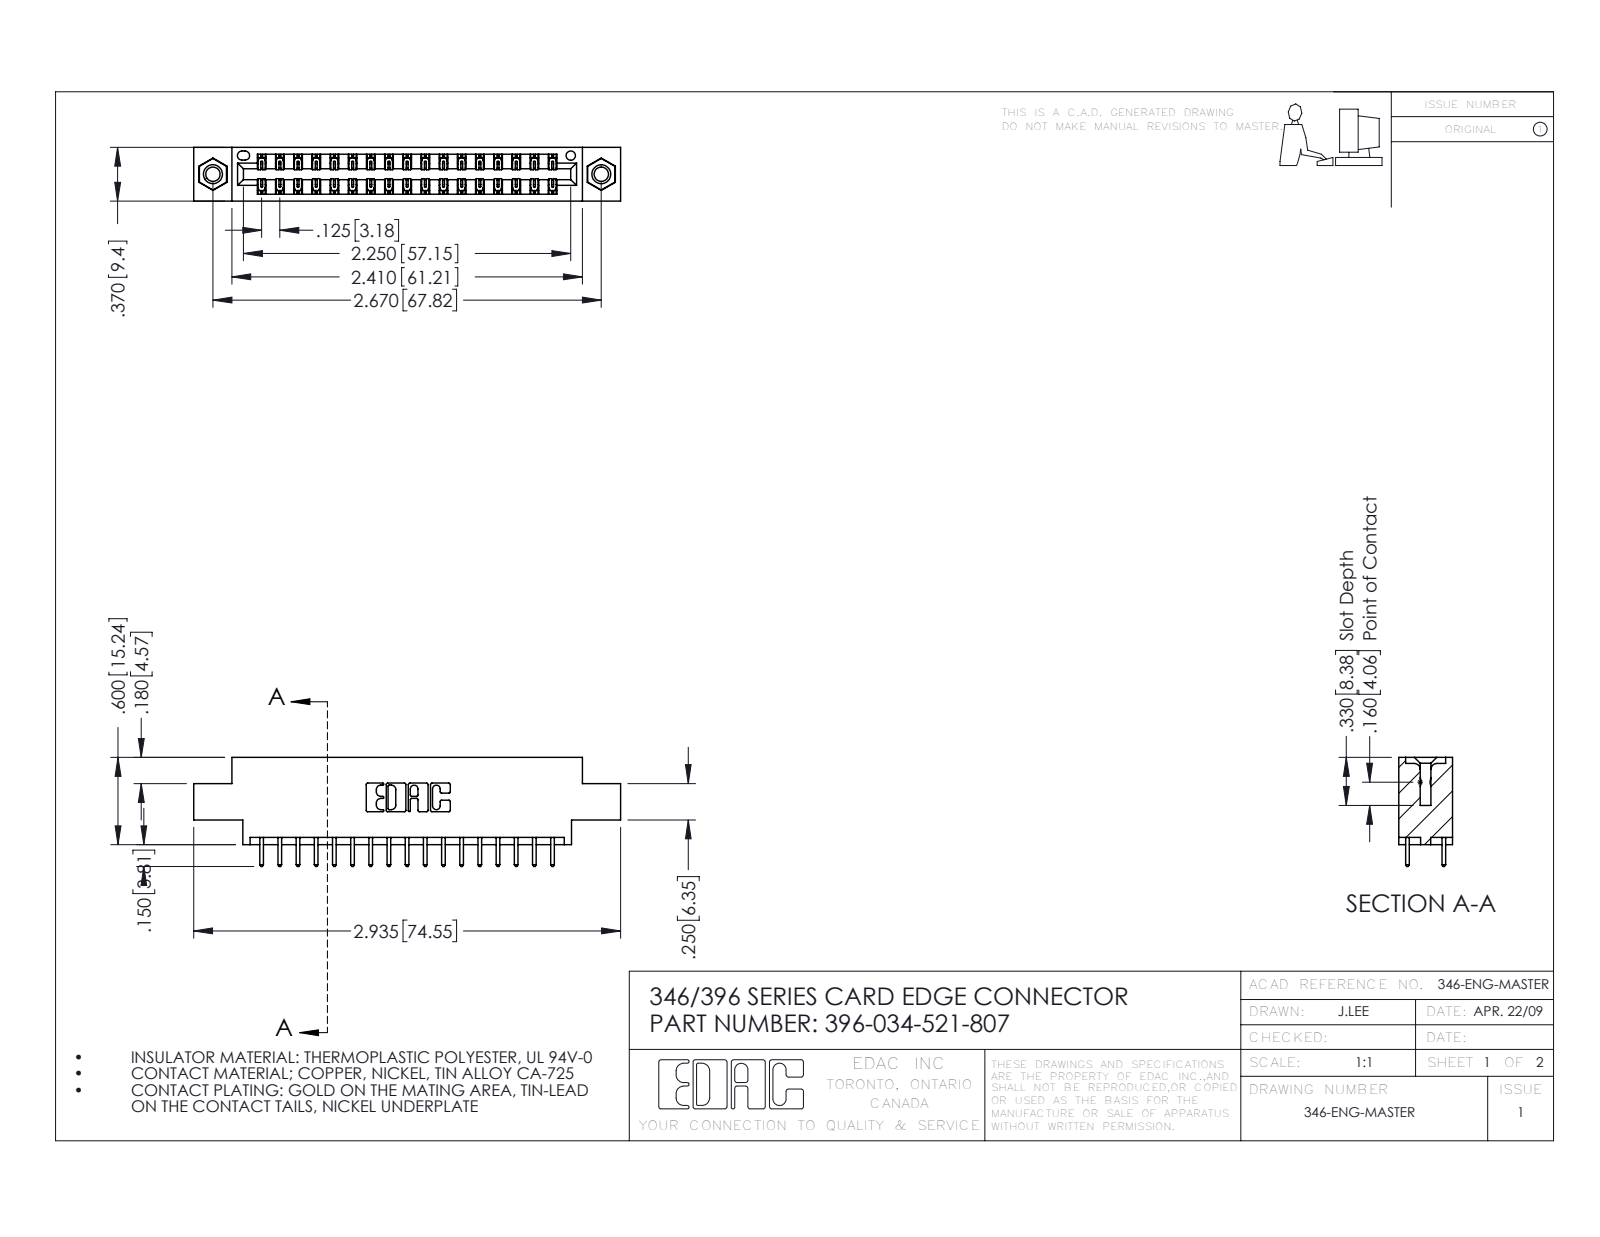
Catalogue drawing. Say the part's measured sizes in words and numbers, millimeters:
The part is named "345-250-001_345-250-005-103; 345-292-001_345-293-121; 396-034-521-807; 346 Part_0.170 Offset - 0.156 Dia-TI". Its 3-D file was written by "SolidWorks 2016 (CONFIG_CONTROL_DESIGN)". It is 37 solids with 1954 faces: 1302 planar, 636 cylindrical and 16 other. Overall it measures 74.5 by 19.1 by 9.4 millimeters. Its volume is 6 900 cubic millimeters and its surface area 9 200 square millimeters. Round holes: 2 of diameter 2.5, 2 of diameter 3.2, 2 of diameter 4, 1 of diameter 1.6. Round bosses or shafts: 2 of diameter 3.9. Partial cylindrical surfaces (rounded edges, fillets, slot ends): 51 of radius 0.2, 34 of radius 0.3, 22 of radius 0.3, 6 of radius 0.2, 6 of radius 0.8, 3 of radius 0.7, 2 of radius 0.4, 2 of radius 0.6. The main face-to-face distances are 1.2, 8.2, 6.4, 9.4, 1.8, 7.6, 0.6, 7, 5.6, 3.8. The hole center spacings are 6.2, 62.6, 67.8.
